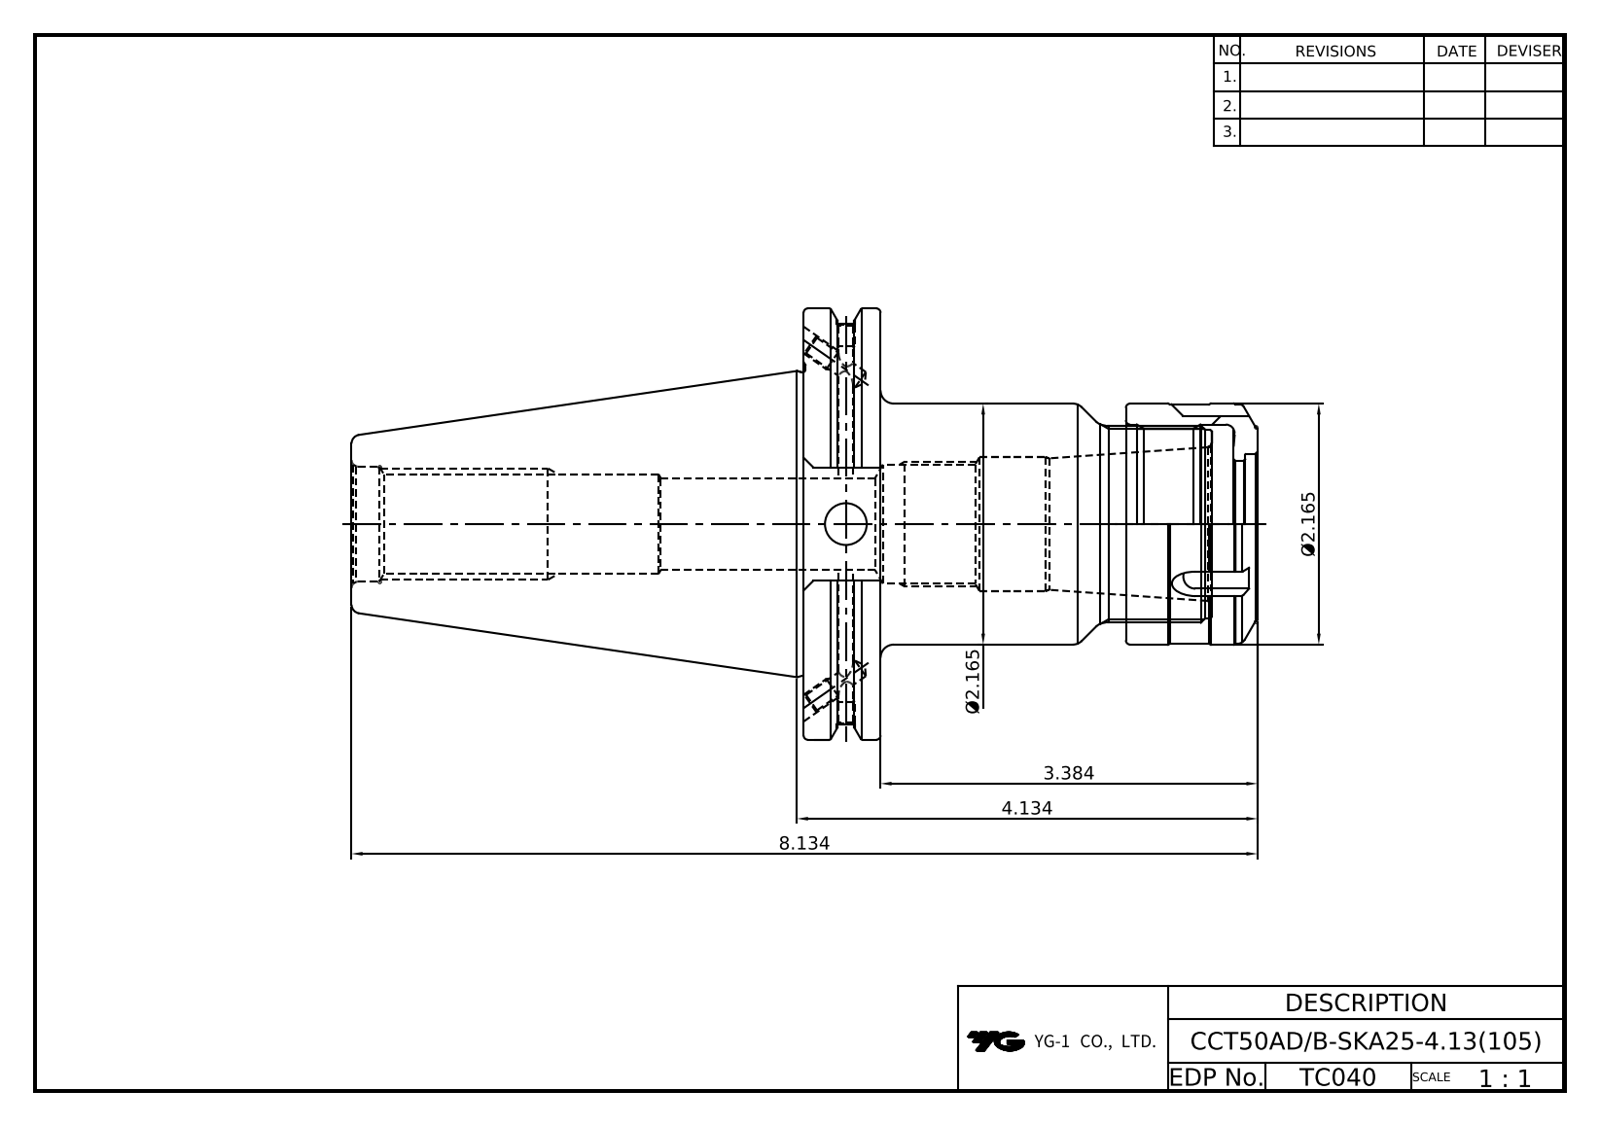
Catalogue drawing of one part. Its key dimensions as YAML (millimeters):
part_name: "LO-CCT50ADB-SKA25-105; SKN25-NUT"
step_written_by: "Autodesk Inventor 2022 (AUTOMOTIVE_DESIGN)"
units: millimeters
bodies: {solids: 2, faces: 167, planar: 62, cylindrical: 42, other: 63}
overall_size: [206.6, 98.42, 94.69]
volume: 453140
surface_area: 75169
round_holes:
  - {diameter: 3.24, count: 2}
  - {diameter: 4.13, count: 2}
  - {diameter: 4.2, count: 2}
  - {diameter: 5, count: 2}
  - {diameter: 9.53, count: 1}
  - {diameter: 21.5, count: 1}
  - {diameter: 21.97, count: 1}
  - {diameter: 26.2, count: 1}
  - {diameter: 26.85, count: 1}
  - {diameter: 30.5, count: 1}
  - {diameter: 34.2, count: 1}
  - {diameter: 36, count: 1}
round_bosses_or_shafts:
  - {diameter: 98.42, count: 1}
  - {diameter: 91.29, count: 1}
  - {diameter: 69.25, count: 1}
  - {diameter: 55, count: 1}
  - {diameter: 54.6, count: 1}
  - {diameter: 45, count: 1}
  - {diameter: 42.98, count: 1}
face_to_face_distances: [17.55, 103.5, 103.1, 85.95, 120.65, 206.6, 176.6, 73.5, 55.95, 30]
